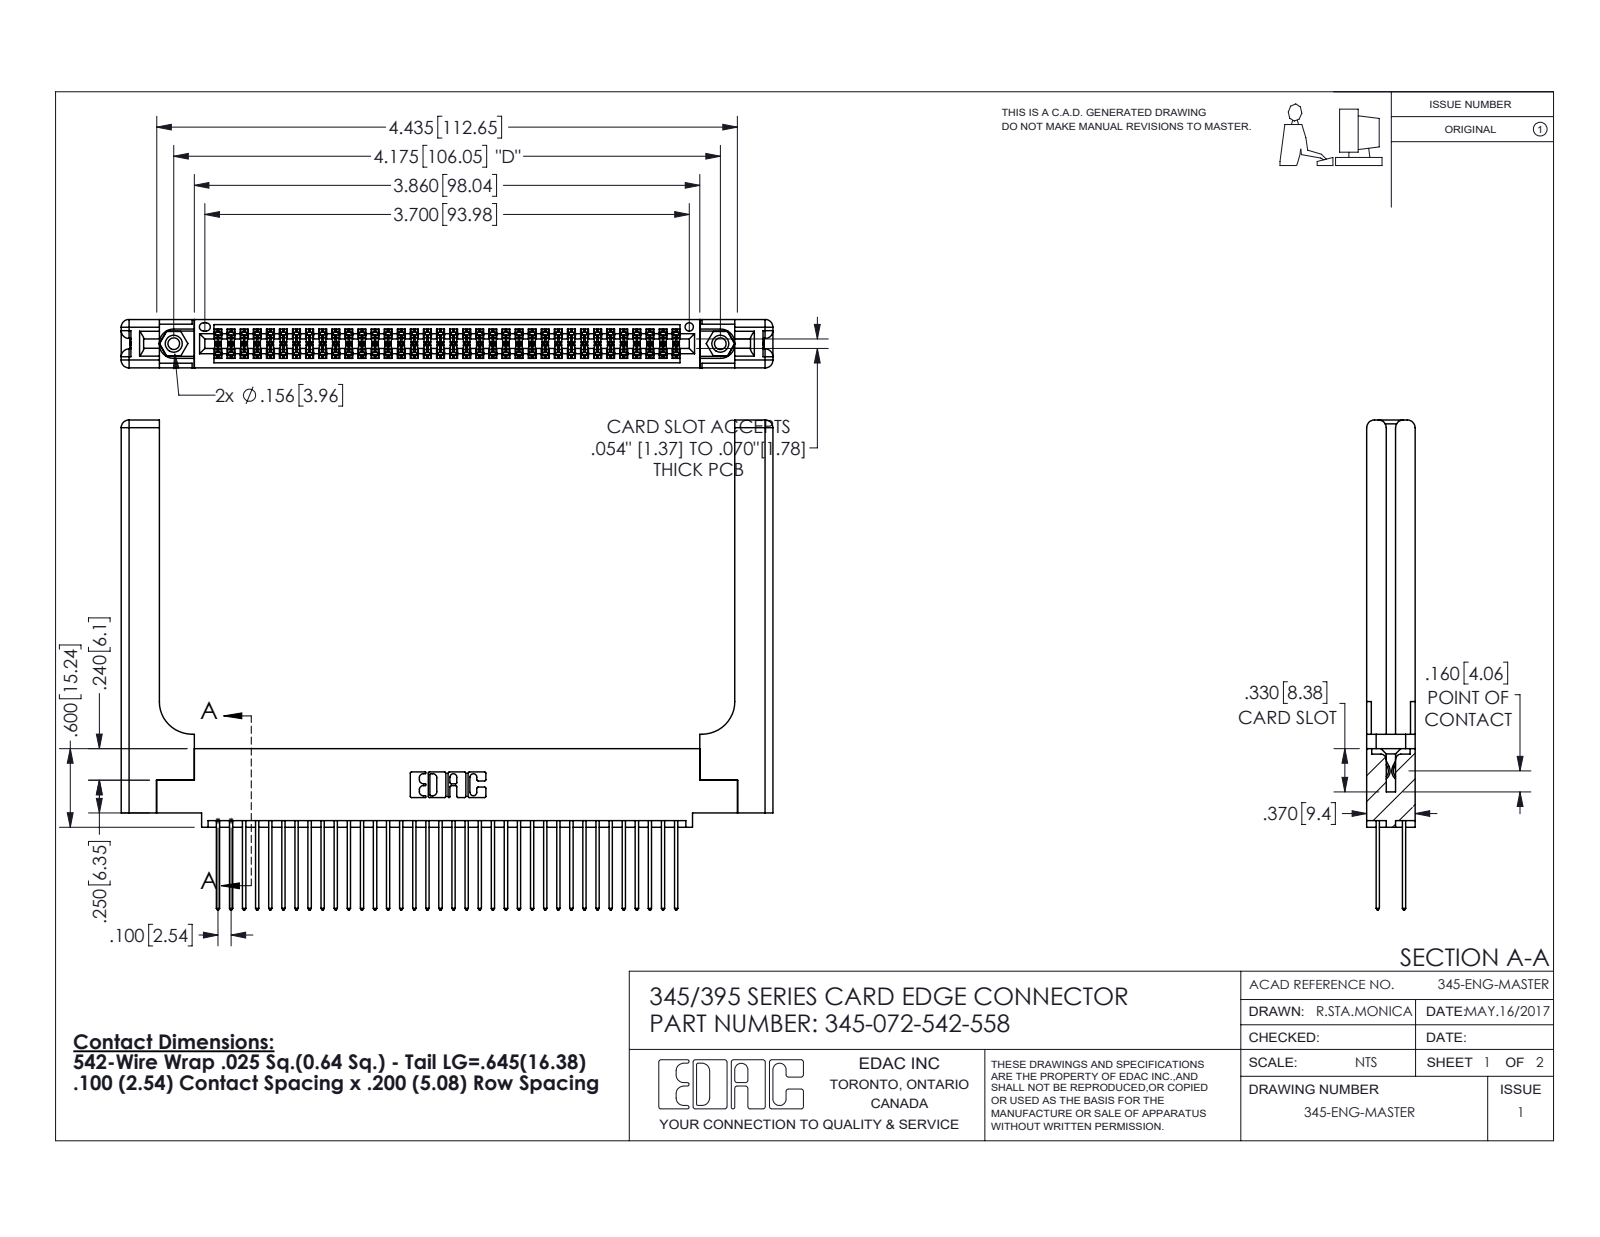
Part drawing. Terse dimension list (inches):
name: 345-220-058_345-220-058; 345 Part_0.110 Offset - 0.156 Dia-TH; 345-072-542-558; 345-292-001_345-293-142 (+1 more)
written by: SolidWorks 2016 (CONFIG_CONTROL_DESIGN)
unit: in
bodies: 77 solids, 3986 faces (2608 planar, 1318 cylindrical, 60 other)
size: 4.979 × 3.742 × 0.37
volume: 1.279 in³; area: 38.86 in²
holes: 2× ⌀0.089, 2× ⌀0.125, 2× ⌀0.156, 1× ⌀0.064
bosses: 2× ⌀0.155
rounds: 108× R0.006, 72× R0.01, 22× R0.01, 16× R0.06, 6× R0.007, 6× R0.031, 3× R0.026, 2× R0.014
face distances: 0.072, 0.298, 0.37, 0.2, 0.098, 0.272, 0.025, 0.225, 0.175, 0.148
hole spacings: 0.27, 3.939, 4.175
